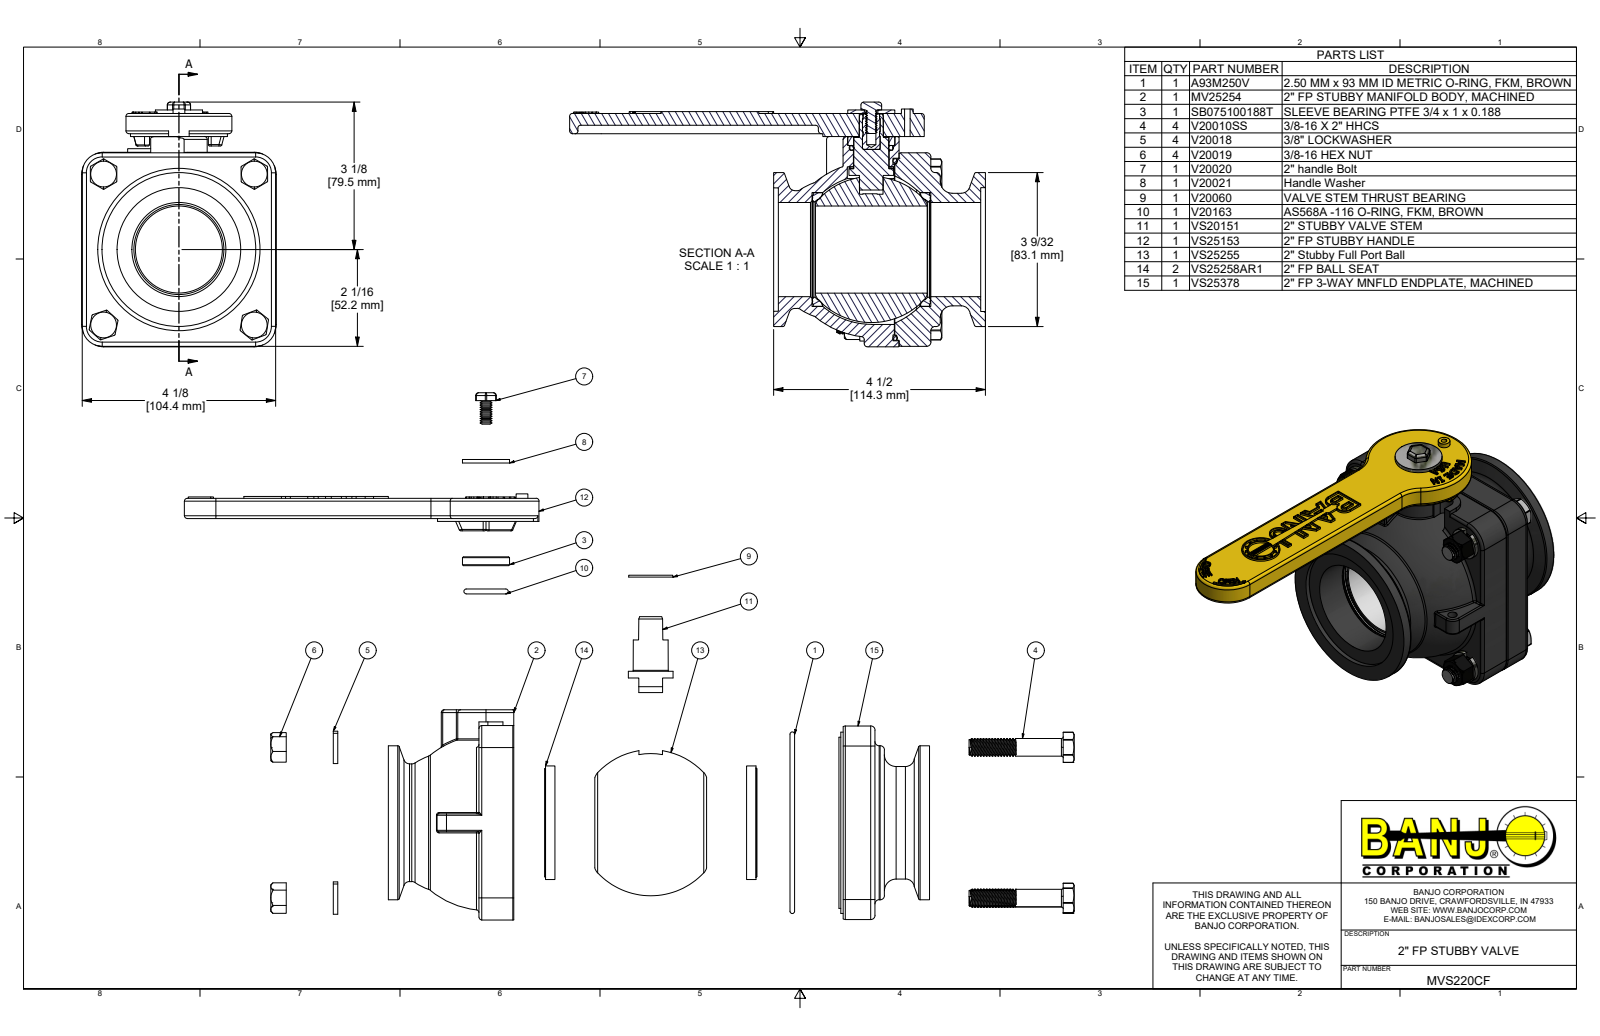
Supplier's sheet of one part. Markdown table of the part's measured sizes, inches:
| quantity | value |
| --- | --- |
| part name | MVS220CF; MV25254; MV25254X; VS20151 (+8 more) |
| STEP written by | Autodesk Inventor 2022 (AUTOMOTIVE_DESIGN) |
| units | inches |
| bodies | 26 solids, 1862 faces (601 planar, 565 cylindrical, 696 other) |
| overall size | 8.835 × 5.196 × 4.13 |
| volume | 36.73 in³ |
| surface area | 279.5 in² |
| round holes (diameter × count) | 0.375 × 5, 0.307 × 4, 0.385 × 4, 0.455 × 4, 0.46 × 4, 0.2 × 2, 0.118 × 1, 0.196 × 1, 0.281 × 1, 0.351 × 1, 0.544 × 1, 0.75 × 1 |
| round bosses / shafts (diameter × count) | 0.324 × 60, 0.687 × 4, 0.375 × 4, 3.85 × 1, 3.635 × 1, 3.625 × 1, 3.27 × 1, 2.5 × 1 |
| partial cylindrical surfaces (radius × count) | 0.06 × 31, 0.03 × 22, 0.09 × 8, 0.162 × 8, 0.32 × 4, 0.425 × 4, 0.468 × 4, 0.2 × 3 |
| main face-to-face distances | 4.12, 0.675, 2.565, 0.25, 0.1, 1.825, 2.475, 1.415, 0.74, 4.11 |
| hole center spacings | 3.202, 2.263, 2.265, 3.2, 3.204, 4.528, 2.041, 2.457 |
